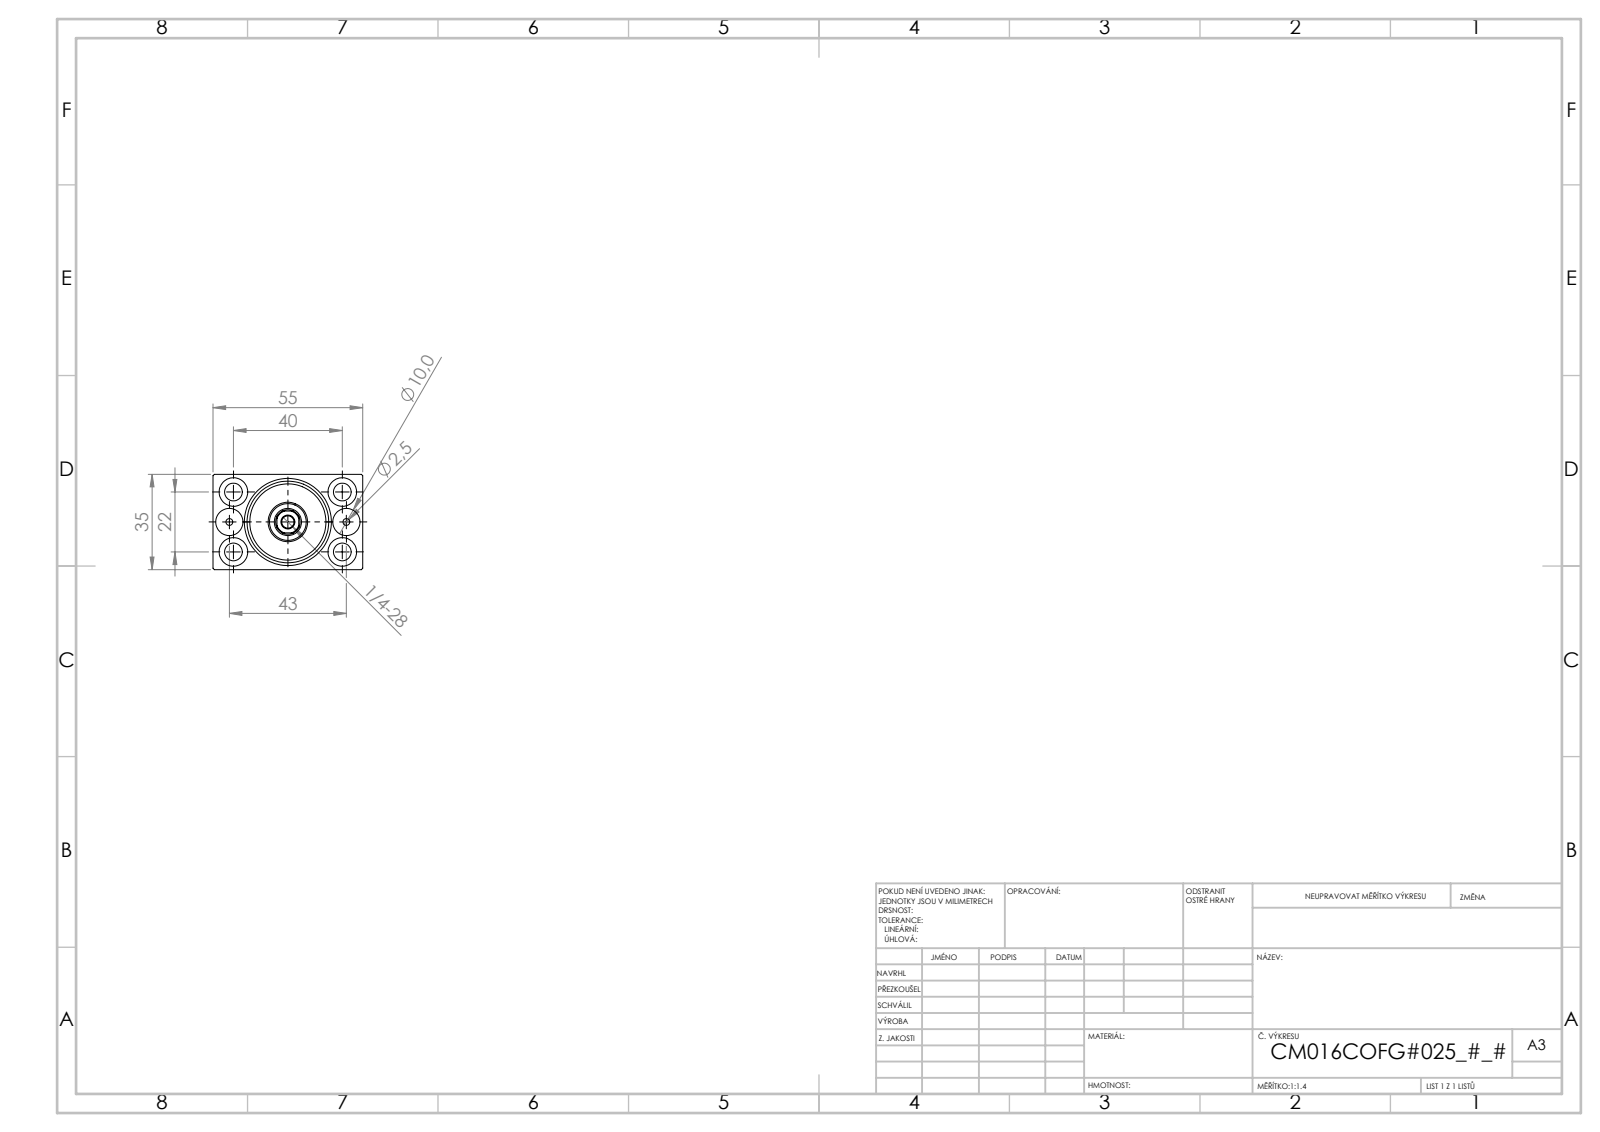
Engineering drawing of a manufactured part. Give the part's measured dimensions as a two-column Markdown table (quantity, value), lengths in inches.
| quantity | value |
| --- | --- |
| part name | V450CM_C_Body; V450CM_VC_B; V450CM_C_VCP |
| STEP written by | SolidWorks 2019 (CONFIG_CONTROL_DESIGN) |
| units | inches |
| bodies | 3 solids, 861 faces (409 planar, 58 cylindrical, 394 other) |
| overall size | 3.15 × 2.165 × 1.378 |
| volume | 7.392 in³ |
| surface area | 52.73 in² |
| round holes (diameter × count) | 0.256 × 4, 0.413 × 4, 0.394 × 3, 0.098 × 2, 0.177 × 1, 0.531 × 1, 0.571 × 1, 0.63 × 1, 0.709 × 1, 1.181 × 1 |
| partial cylindrical surfaces (radius × count) | 0.177 × 1 |
| main face-to-face distances | 1.378, 2.165, 2.598, 0.197, 0.079, 2.795, 0.118, 2.402, 0.315, 2.913 |
| hole center spacings | 0.437, 0.899, 1.69, 0.846, 0.866, 1.575, 1.797, 1.693 |
